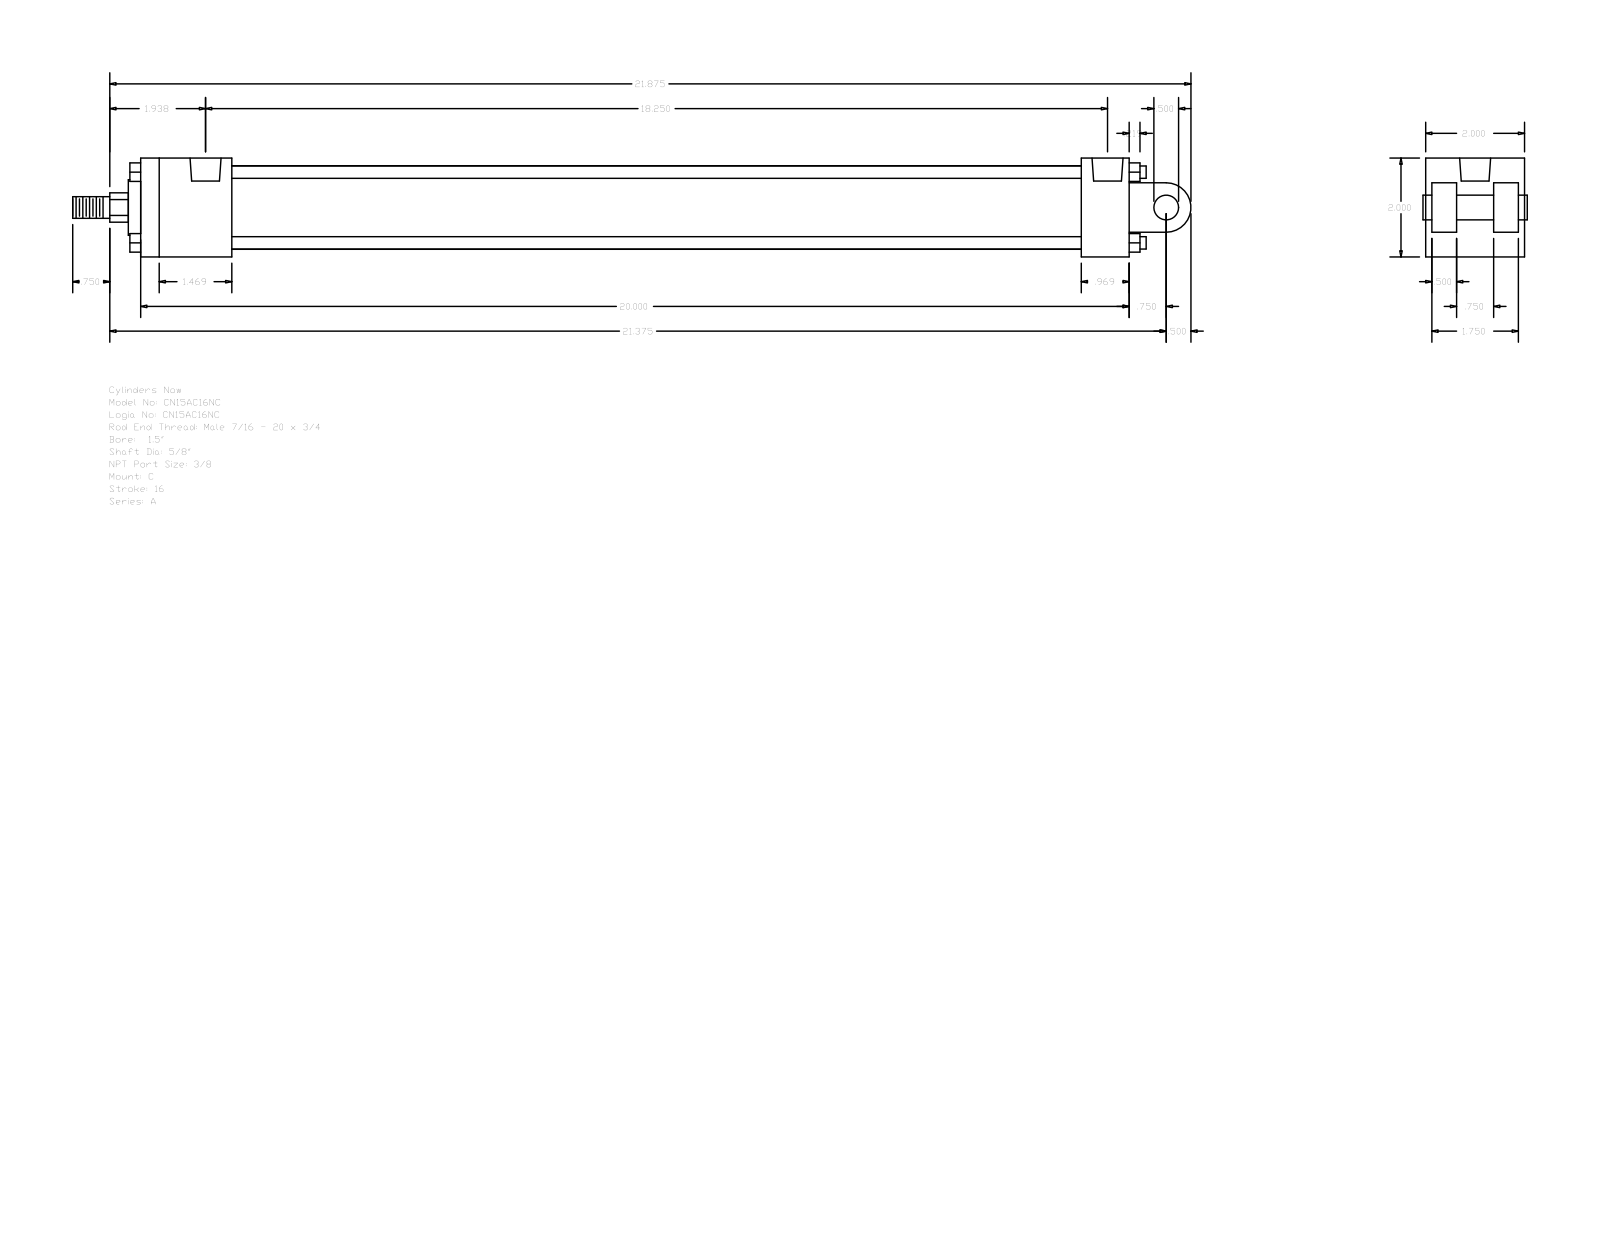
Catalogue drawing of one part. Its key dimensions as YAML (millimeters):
part_name: "A_C__0150_0.625"
step_written_by: "GSSL Pune (CONFIG_CONTROL_DESIGN)"
units: millimeters
bodies: {solids: 0, faces: 135, planar: 102, cylindrical: 33, other: 0}
overall_size: [574.67, 50.8, 50.8]
round_holes:
  - {diameter: 5.56, count: 4}
  - {diameter: 15.93, count: 2}
round_bosses_or_shafts:
  - {diameter: 6.35, count: 4}
  - {diameter: 42.93, count: 1}
  - {diameter: 28.57, count: 1}
  - {diameter: 15.88, count: 1}
  - {diameter: 12.7, count: 1}
  - {diameter: 11.11, count: 1}
partial_cylinders:
  - {radius: 7.54, count: 1}
  - {radius: 12.7, count: 1}
face_to_face_distances: [50.8, 12.7, 508, 34.93, 3.17, 47.63, 15.87, 31.76, 483.39, 24.61]
hole_center_spacings: [3.97, 455.61, 459.58, 463.55]
